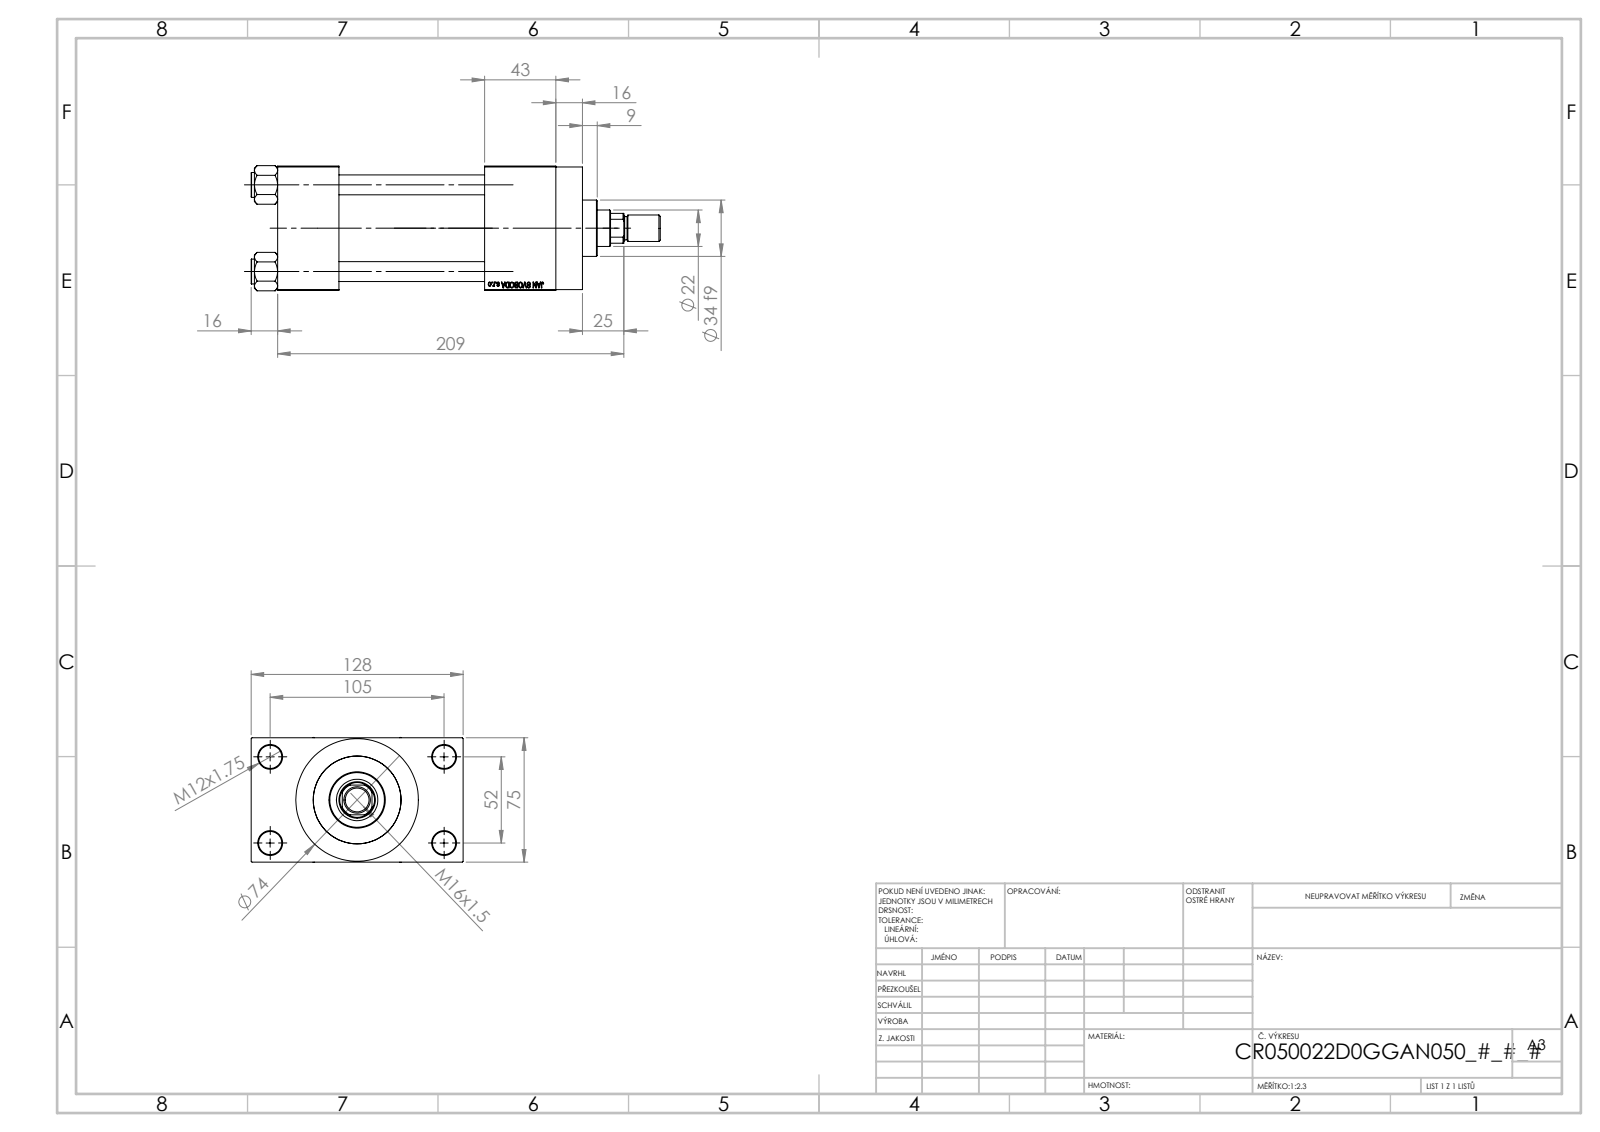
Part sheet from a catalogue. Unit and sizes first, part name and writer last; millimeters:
Units: millimetres
Overall size (bounding box): 247 × 128 × 75.54
Round holes (diameter × count): ⌀12 ×4, ⌀14 ×4, ⌀7 ×2, ⌀20.96 ×2, ⌀30 ×2, ⌀10.5 ×1, ⌀22 ×1, ⌀25 ×1, ⌀41 ×1, ⌀50 ×1, ⌀53 ×1
Round bosses / shafts (diameter × count): ⌀15 ×4, ⌀74 ×1, ⌀56 ×1, ⌀34 ×1, ⌀16 ×1, ⌀14 ×1
Partial cylindrical surfaces — rounded edges, fillets, slot ends (radius × count): R10.5 ×1
Main face-to-face distances: 75, 88, 125, 37, 26.5, 101.5, 168, 131, 43, 16
Hole centre spacings: 26.35, 36.98, 52.3, 58.43, 58.59, 78.65, 94.37, 52
Volume: 850 810 mm³ · Surface area: 183 076 mm²
Bodies: 12 solids, 1118 faces (501 planar, 93 cylindrical, 524 other)
Part name (STEP PRODUCT): V215_VC_A; NUT_M5_D; V215CR_D_TYCINKA; ROD_END_AH (+2 more)
STEP written by: SolidWorks 2019 (CONFIG_CONTROL_DESIGN)
